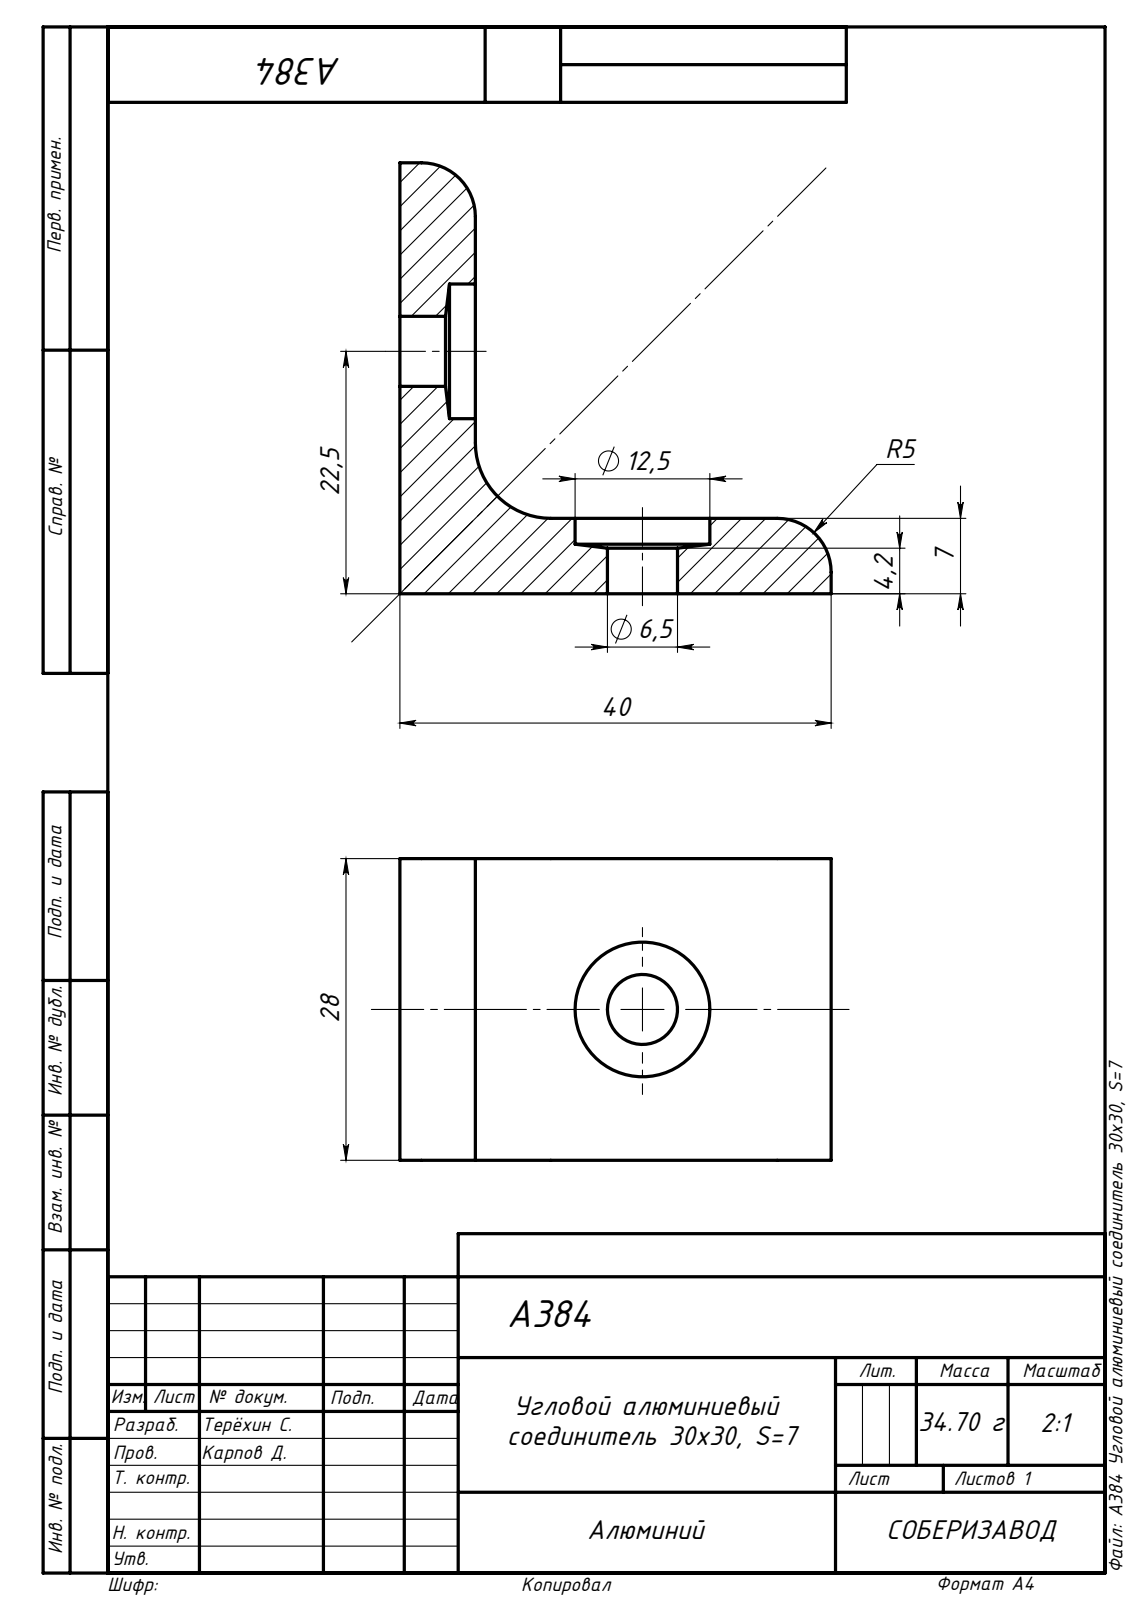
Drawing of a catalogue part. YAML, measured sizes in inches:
part_name: "A384 Угловой алюминиевый соединитель 30х30, S=7"
step_written_by: "SolidWorks 2020 (AUTOMOTIVE_DESIGN)"
units: inches
bodies: {solids: 1, faces: 23, planar: 8, cylindrical: 11, other: 4}
overall_size: [1.575, 1.575, 1.102]
volume: 0.816
surface_area: 8.567
round_holes:
  - {diameter: 0.256, count: 2}
  - {diameter: 0.492, count: 2}
partial_cylinders:
  - {radius: 0.197, count: 2}
  - {radius: 0.276, count: 1}
face_to_face_distances: [0.276, 1.102, 1.575, 1.299]
